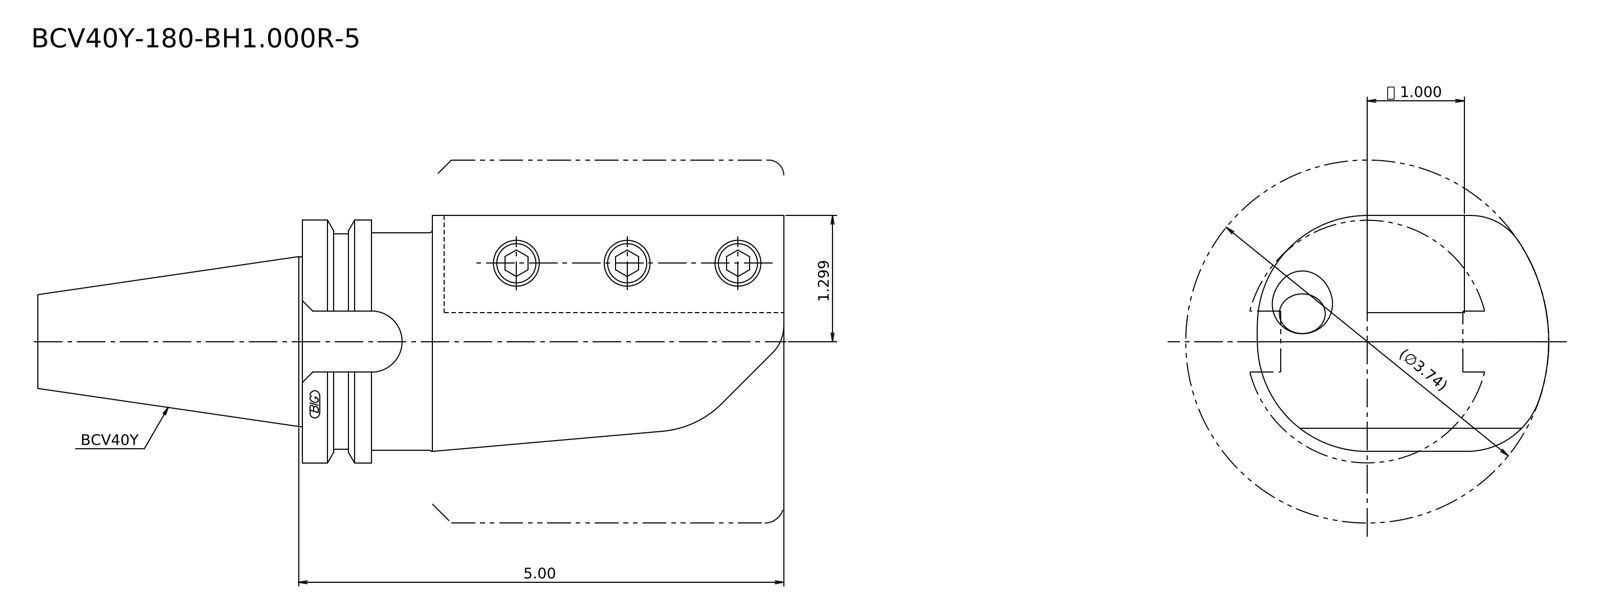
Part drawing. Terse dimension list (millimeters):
written by: Kubotek KeyCreator 2011 V10.0.2 (22737) (automotive_design)
unit: mm
bodies: 1 solid, 29 faces (15 planar, 10 cylindrical, 4 other)
size: 195.25 × 79.25 × 64.75
volume: 446 663 mm³; area: 47 040 mm²
bosses: 1× ⌀63.5, 1× ⌀57, 1× ⌀56.36, 1× ⌀44.45
rounds: 2× R28.75, 1× R15, 1× R20, 1× R47.5
face distances: 25.4, 126, 92, 34, 88.9, 3.1, 37.1, 107.95, 19.05, 15.95
